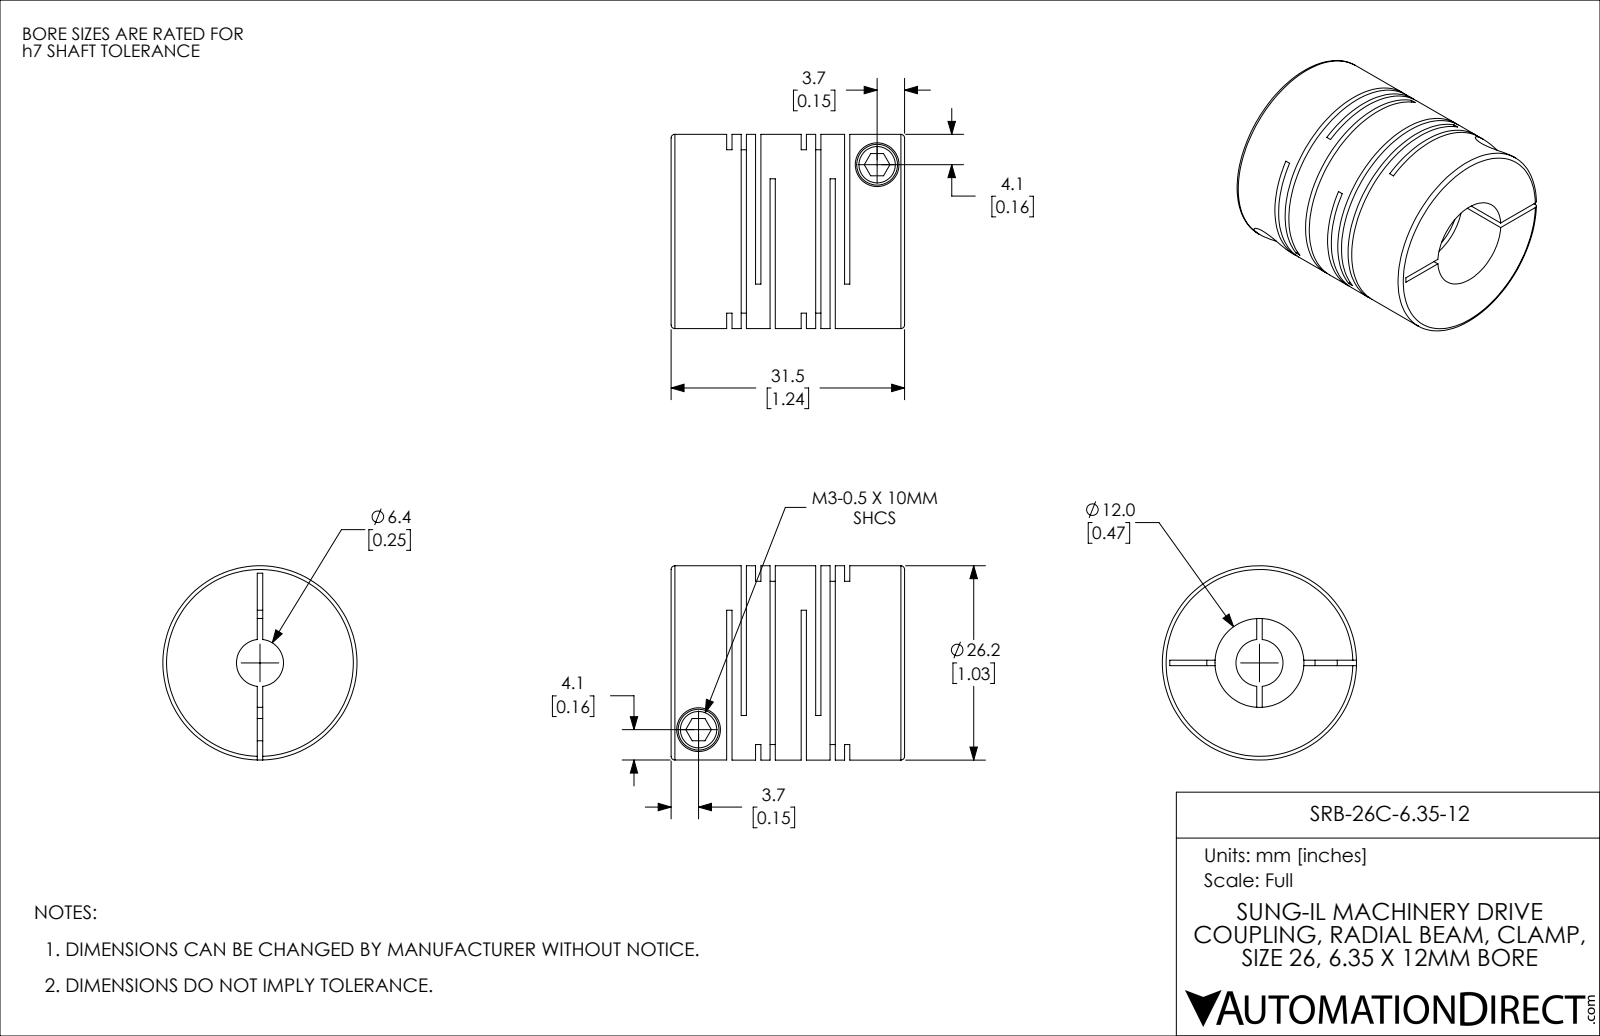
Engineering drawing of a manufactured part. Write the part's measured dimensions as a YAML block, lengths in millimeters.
part_name: "SRB-26C-6.35-12"
step_written_by: "SolidWorks 2021 (CONFIG_CONTROL_DESIGN)"
units: millimeters
bodies: {solids: 1, faces: 114, planar: 60, cylindrical: 42, other: 12}
overall_size: [31.5, 26.2, 26.2]
volume: 11652
surface_area: 10318
round_holes:
  - {diameter: 3, count: 2}
  - {diameter: 5.9, count: 2}
  - {diameter: 6.35, count: 1}
  - {diameter: 12, count: 1}
round_bosses_or_shafts:
  - {diameter: 5.5, count: 2}
  - {diameter: 26.2, count: 1}
face_to_face_distances: [1.95, 10.05, 0.71, 3.9, 8.1, 12, 1.24, 2.66, 9.34, 13.95]
